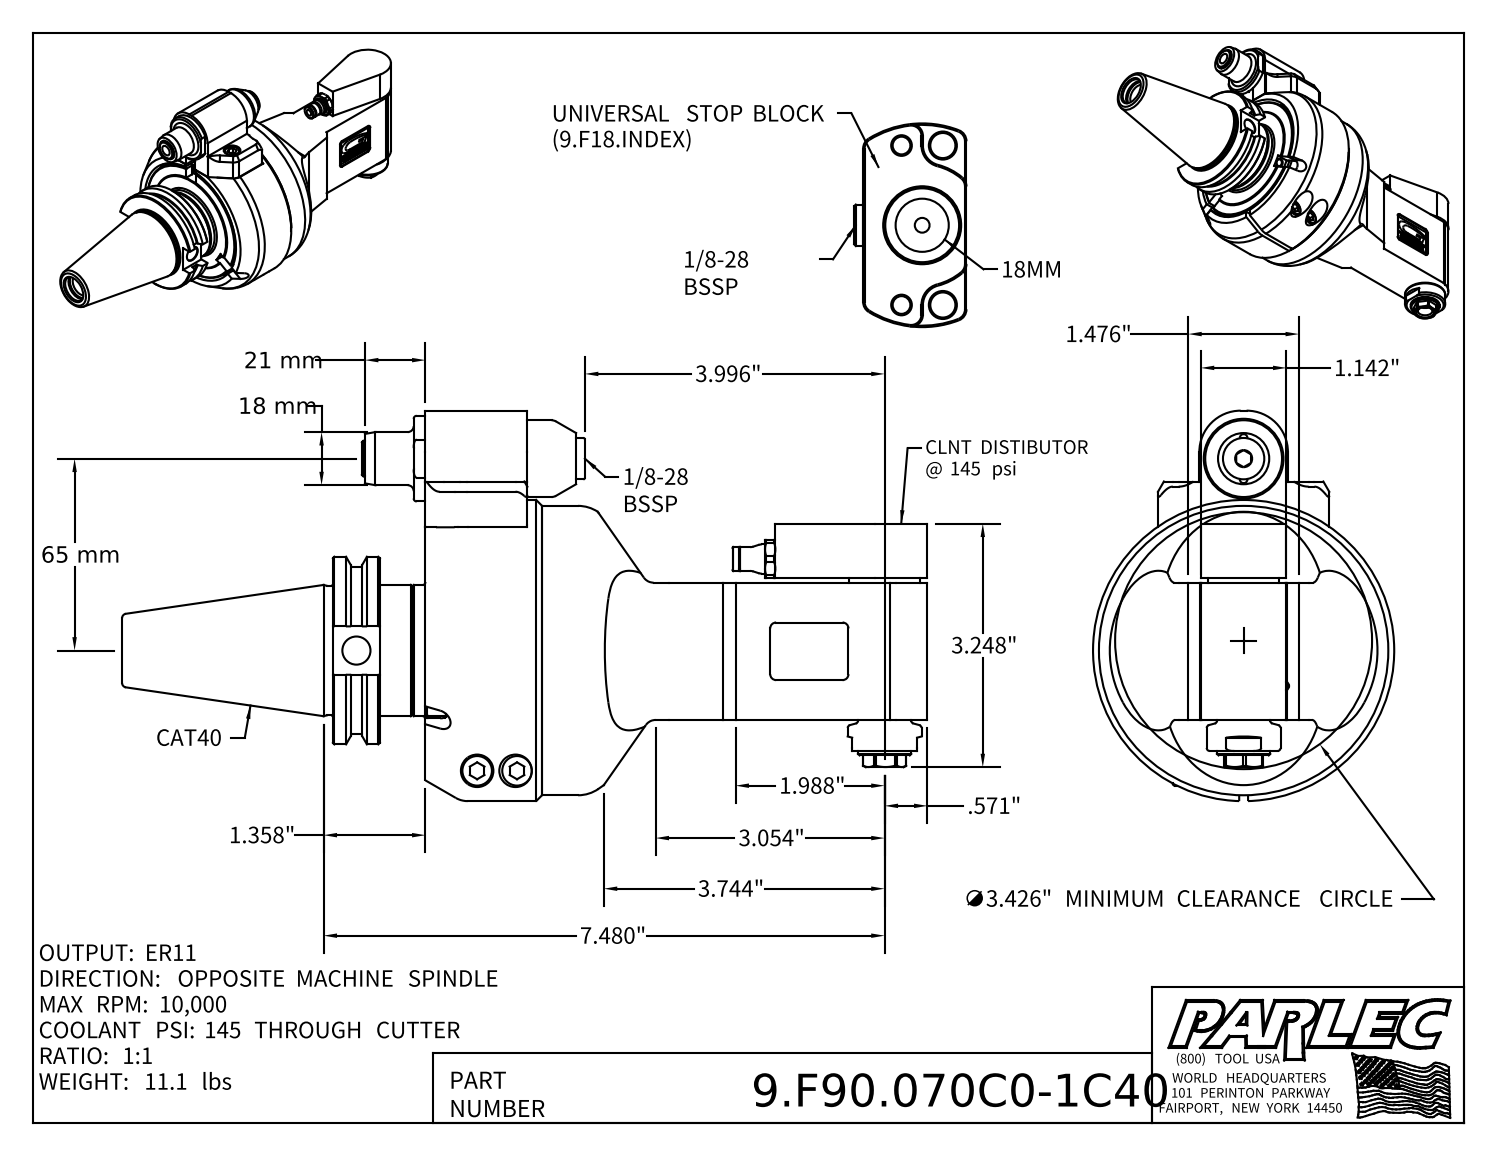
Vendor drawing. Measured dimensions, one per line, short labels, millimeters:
name: 9.F90.070C0-1C40; F90-7C; 9_GA1_446_2 (Type 1, C40, 65mm)
written by: Autodesk Inventor 2022 (AUTOMOTIVE_DESIGN)
unit: mm
bodies: 5 solids, 526 faces (240 planar, 145 cylindrical, 141 other)
size: 272.7 × 132.2 × 102
volume: 834 600 mm³; area: 142 300 mm²
holes: 21× ⌀8.5, 2× ⌀2.6, 2× ⌀4.2, 2× ⌀5, 2× ⌀10.4, 2× ⌀11, 1× ⌀2.5, 1× ⌀3, 1× ⌀4, 1× ⌀6.5, 1× ⌀7, 1× ⌀7.5
bosses: 4× ⌀10, 4× ⌀6, 2× ⌀18, 2× ⌀8, 2× ⌀2.5, 1× ⌀102, 1× ⌀98, 1× ⌀77
rounds: 12× R2, 4× R4, 2× R0.5, 2× R1, 2× R3.5, 2× R5, 2× R14, 2× R14.5
face distances: 32, 0.5, 7, 39.5, 46.5, 7.5, 65.3, 29, 1.5, 18.7
hole spacings: 38.5, 37.3, 46.3, 54.5, 76.3, 10.7, 67.3, 74
